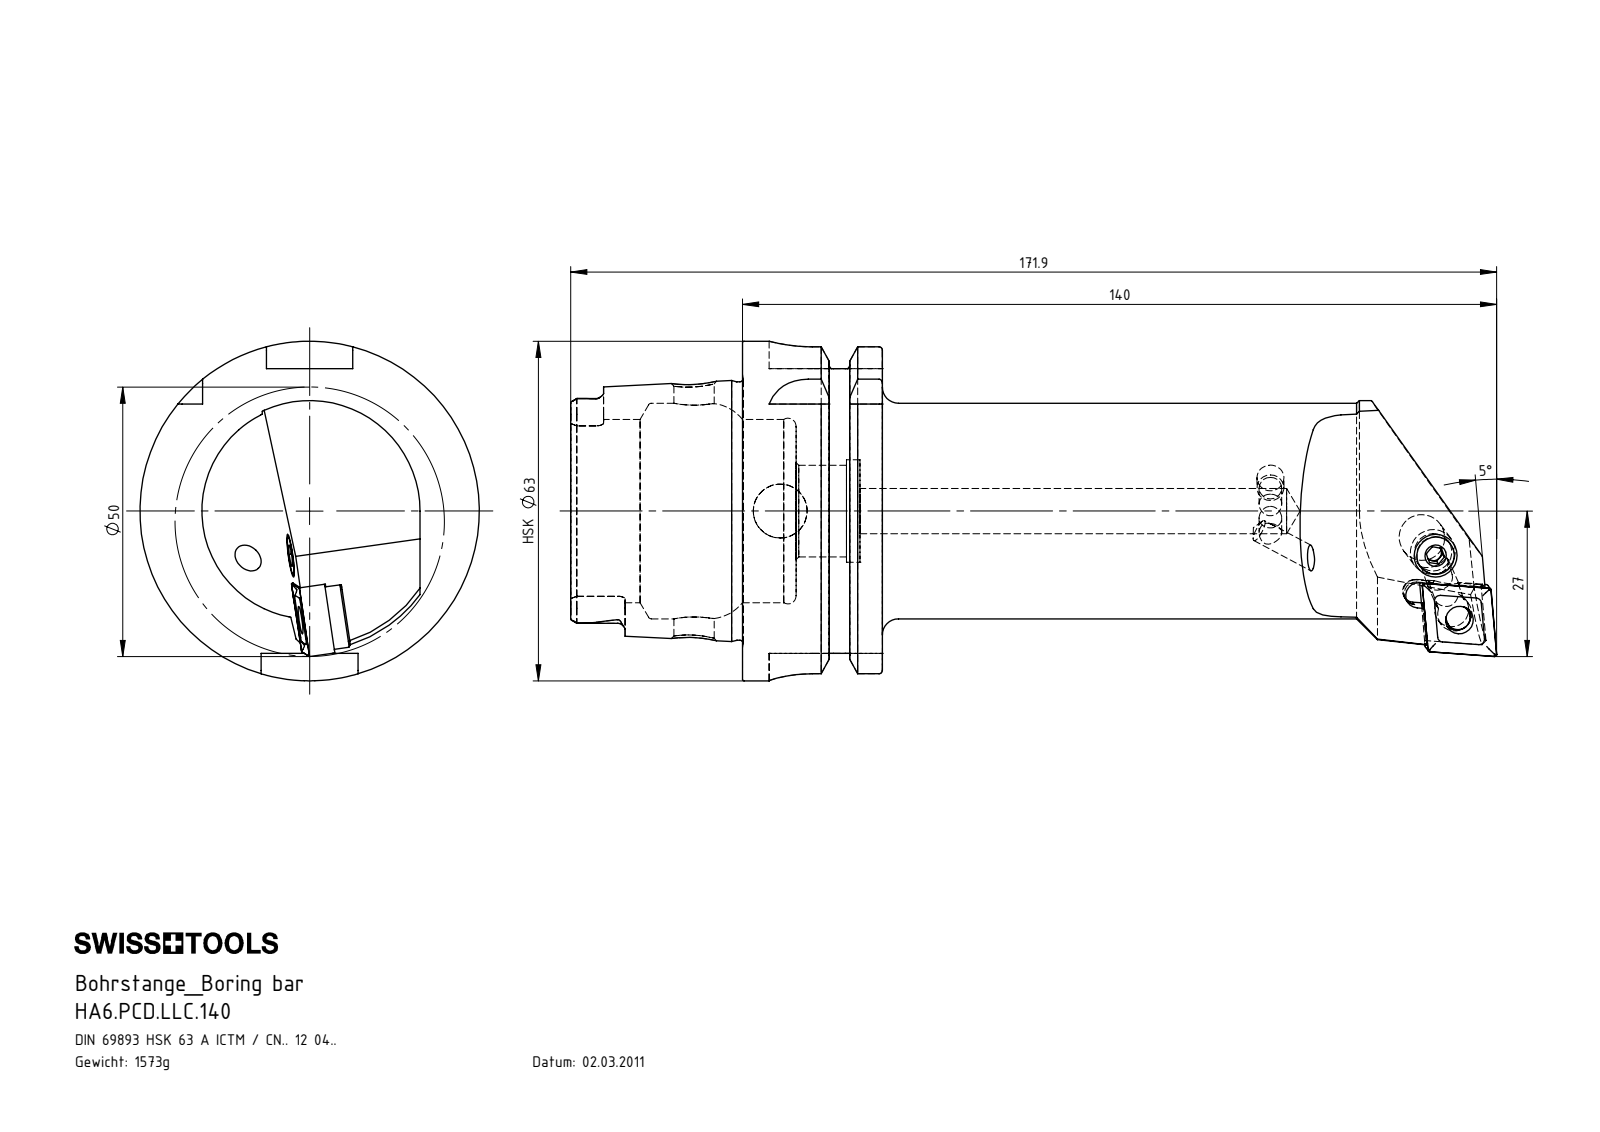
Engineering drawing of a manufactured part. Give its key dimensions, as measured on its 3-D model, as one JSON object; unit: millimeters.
{"part_name": "WCD; WCD-ER3.101.000_A; WCD-ER4.101.017_A; CNMG120404 (+4 more)", "step_written_by": "SolidWorks 2017 (AUTOMOTIVE_DESIGN)", "units": "millimeters", "bodies": {"solids": 7, "faces": 364, "planar": 113, "cylindrical": 102, "other": 149}, "overall_size": [171.9, 63, 63], "volume_mm3": 200745, "surface_area_mm2": 40682, "round_holes": [[4.2, 2], [8.4, 2], [4, 1], [5, 1], [5.16, 1], [6.4, 1], [7, 1], [7.5, 1], [10, 1], [17, 1], [19, 1], [34, 1]], "round_bosses_or_shafts": [[63, 1], [54.95, 1], [47.94, 1], [8, 1], [7.9, 1], [6.4, 1], [5, 1], [4.5, 1]], "partial_cylinders_radius": [[1.4, 6], [0.4, 4], [1, 4], [8, 4], [2.5, 2], [2.82, 2], [2.88, 2], [2.1, 1]], "face_to_face_distances": [25.95, 16, 9.95, 31.9, 41.85, 57.85, 52.8, 21.8, 11.85, 4.49], "hole_center_spacings": [12.81, 12.87]}
